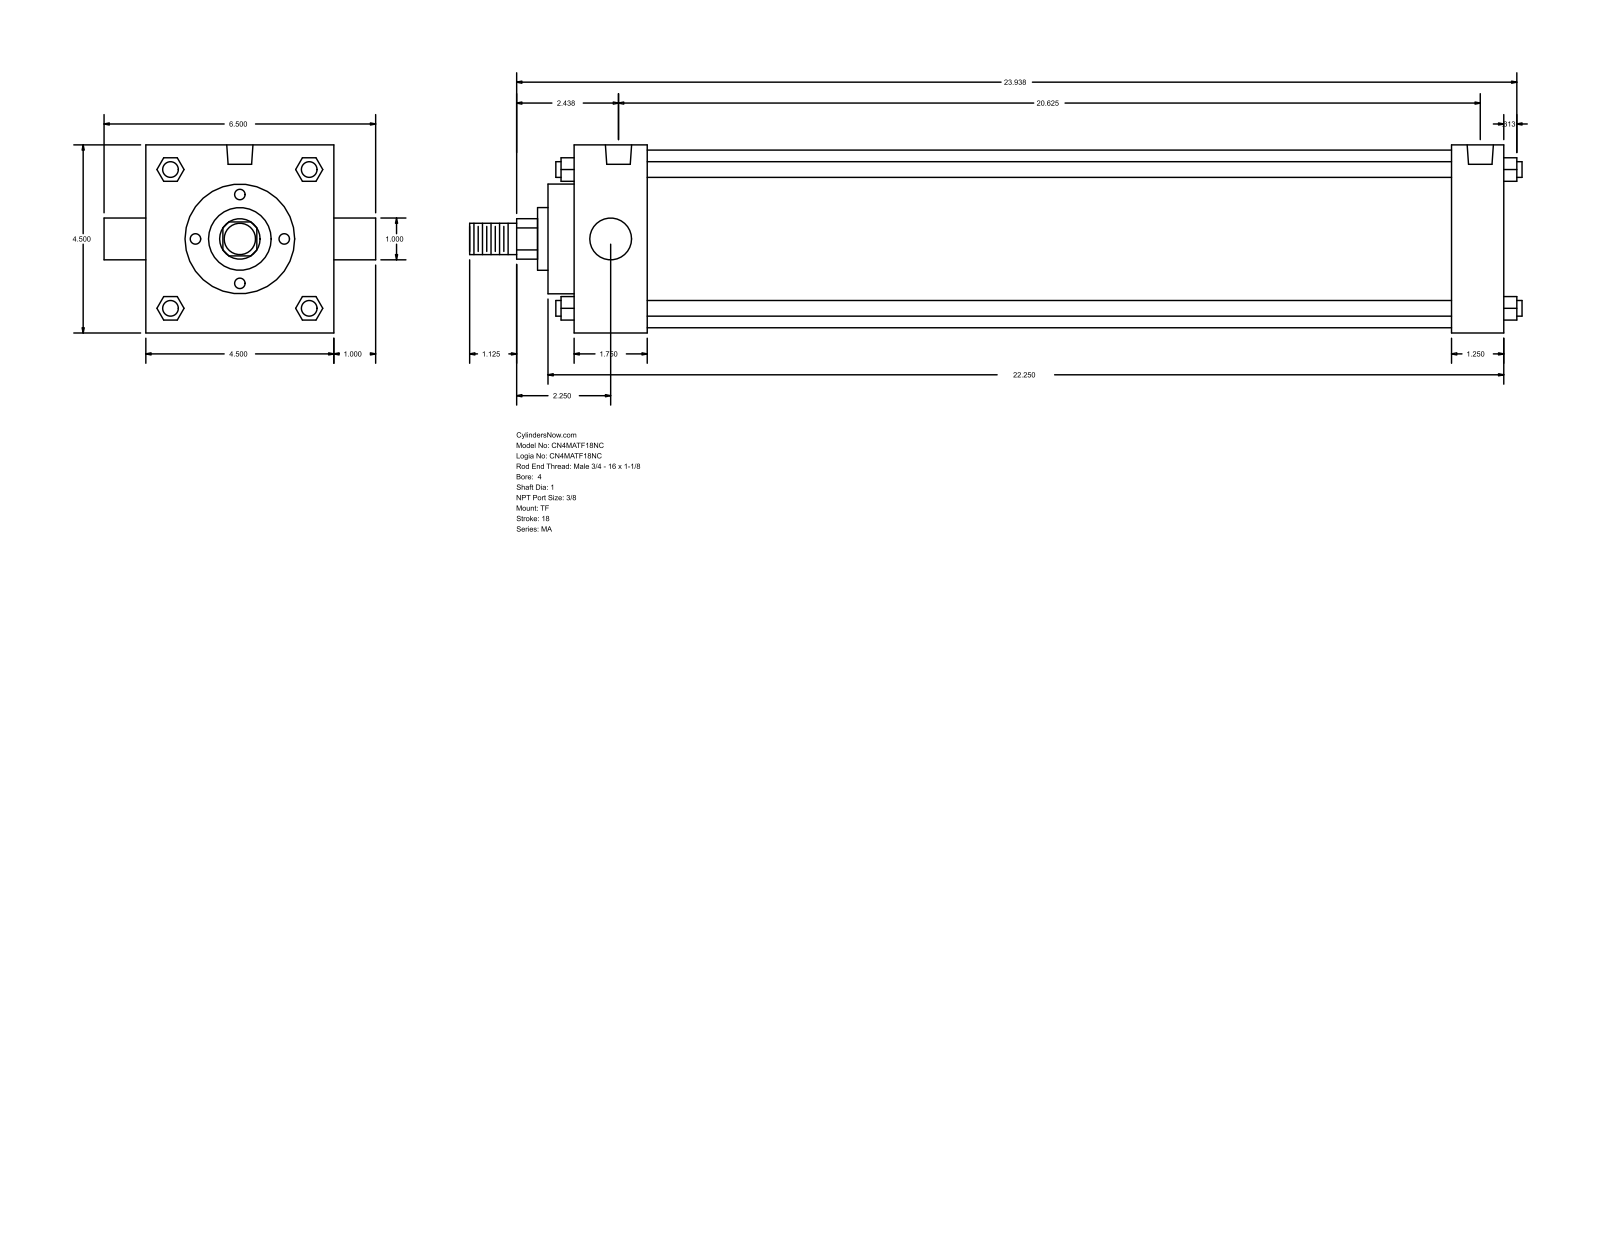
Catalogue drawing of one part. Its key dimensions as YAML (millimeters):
part_name: "MA_TF__0400_1"
step_written_by: "GSSL Pune (CONFIG_CONTROL_DESIGN)"
units: millimeters
bodies: {solids: 0, faces: 122, planar: 93, cylindrical: 29, other: 0}
overall_size: [639.76, 165.1, 114.3]
round_holes:
  - {diameter: 11.11, count: 3}
  - {diameter: 15.93, count: 2}
round_bosses_or_shafts:
  - {diameter: 9.53, count: 4}
  - {diameter: 25.4, count: 2}
  - {diameter: 107.95, count: 1}
  - {diameter: 66.67, count: 1}
  - {diameter: 38.1, count: 1}
  - {diameter: 19.05, count: 1}
partial_cylinders:
  - {radius: 12.29, count: 1}
face_to_face_distances: [114.3, 565.16, 533.41, 31.75, 44.46, 488.95, 520.7, 15.87, 60.33, 549.28]
hole_center_spacings: [4.76, 4.77, 514.35, 519.11, 519.12, 523.88]
